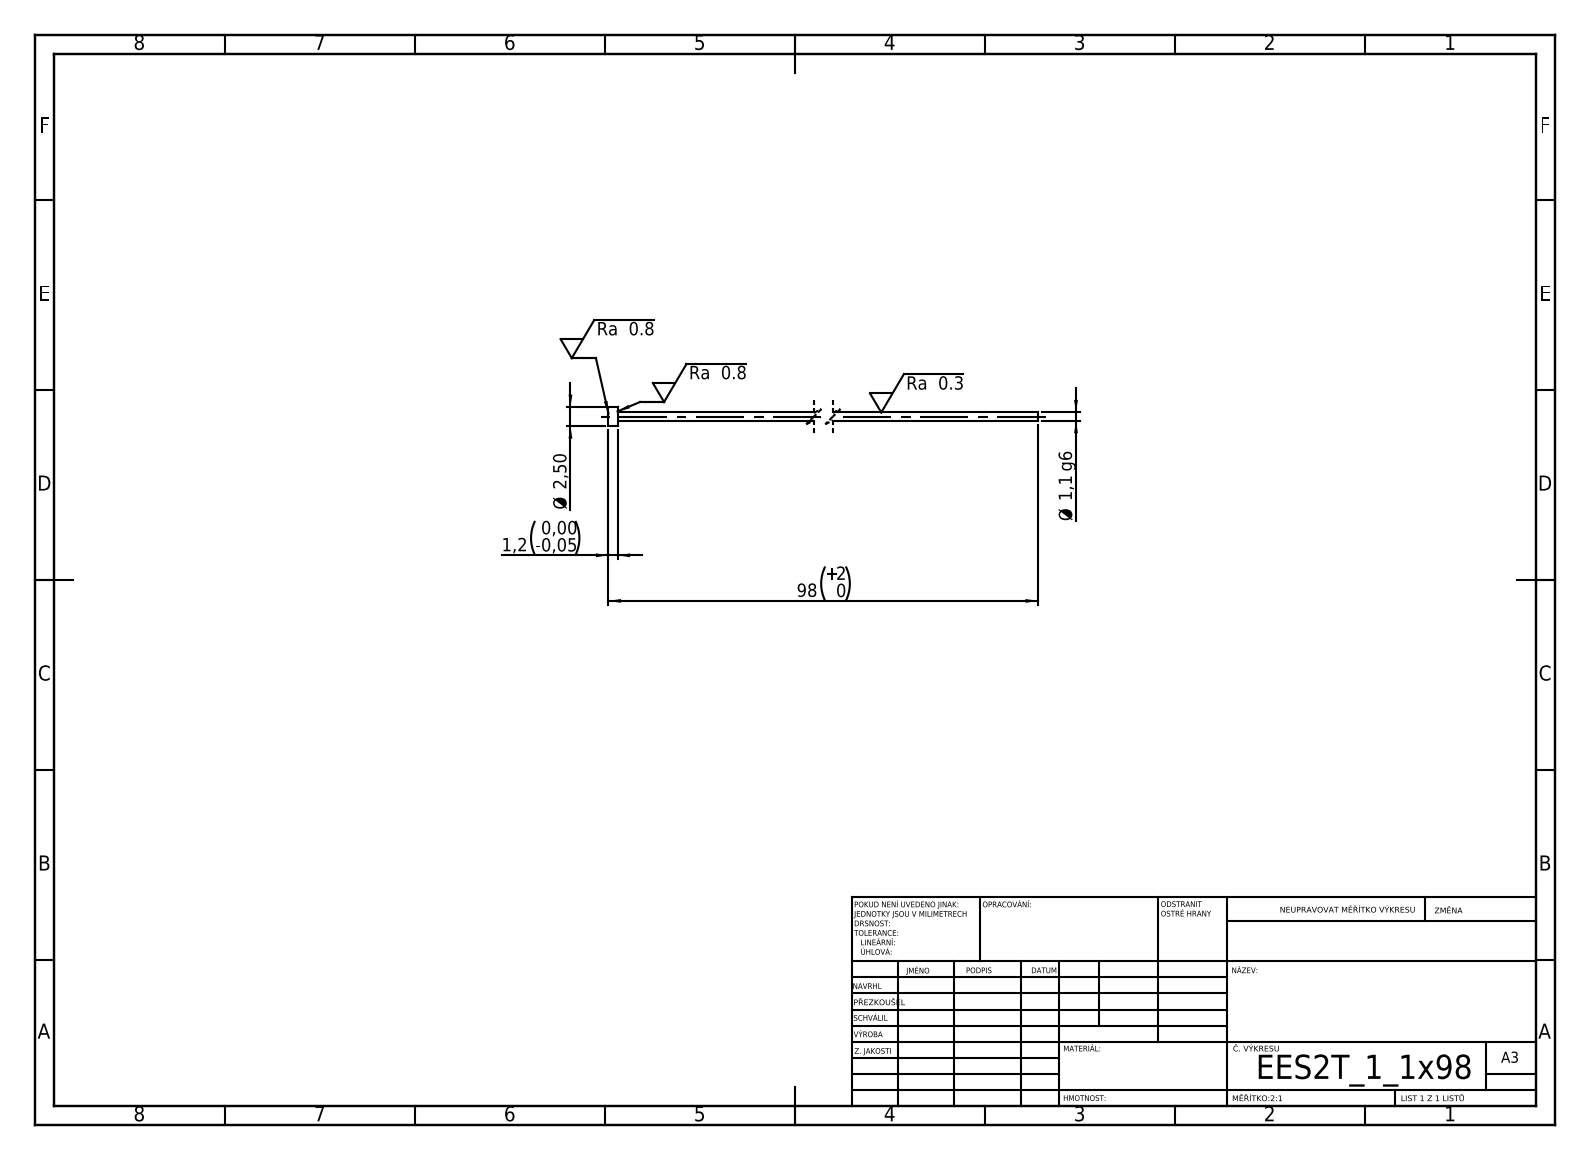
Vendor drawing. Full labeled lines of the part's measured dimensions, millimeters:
STEP written by: SolidWorks 2019 (CONFIG_CONTROL_DESIGN)
Units: millimetres
Bodies: 1 solid, 7 faces (3 planar, 4 cylindrical, 0 other)
Overall size (bounding box): 98 × 2.5 × 2.5
Volume: 98 mm³ · Surface area: 354 mm²
Round bosses / shafts (diameter × count): ⌀2.5 ×1, ⌀1.1 ×1
Main face-to-face distances: 1.2, 98, 96.8
